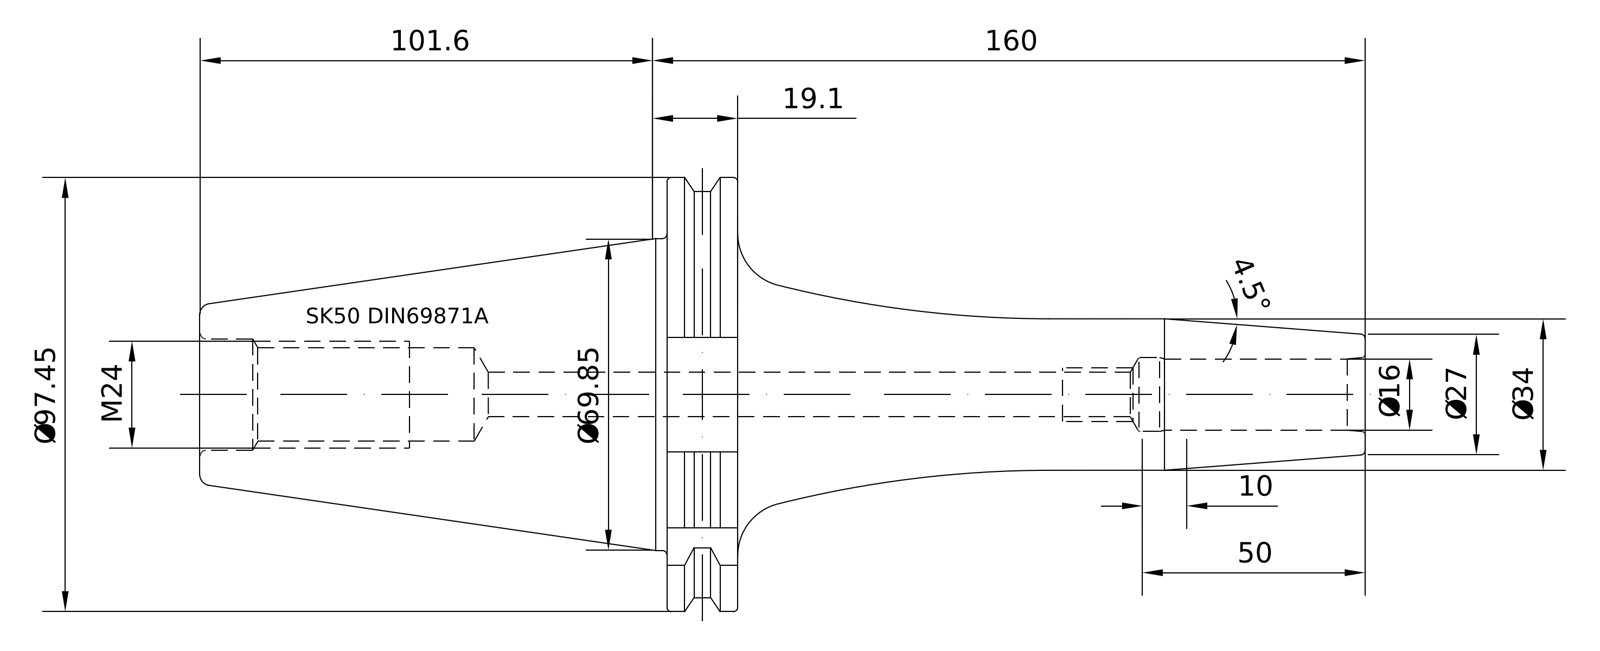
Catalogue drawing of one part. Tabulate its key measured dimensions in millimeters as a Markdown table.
| quantity | value |
| --- | --- |
| part name | 50-442-16 |
| STEP written by | PRO/ENGINEER BY PARAMETRIC TECHNOLOGY CORPORATION, 2010430 (CONFIG_CONTROL_DESIGN) |
| units | millimeters |
| bodies | 1 solid, 95 faces (21 planar, 24 cylindrical, 50 other) |
| overall size | 261.6 × 97.47 × 94 |
| volume | 481 485 mm³ |
| surface area | 59 165 mm² |
| round holes (diameter × count) | 16 × 1, 20.75 × 1, 25.01 × 1, 25.7 × 1 |
| round bosses / shafts (diameter × count) | 91 × 1, 69.15 × 1, 34 × 1, 24.01 × 1 |
| partial cylindrical surfaces (radius × count) | 1.75 × 1, 48.74 × 1 |
| main face-to-face distances | 15.85, 72.8, 104.8, 120.65, 25.8, 261.6, 156.8, 140.95, 211.6, 106.8 |
